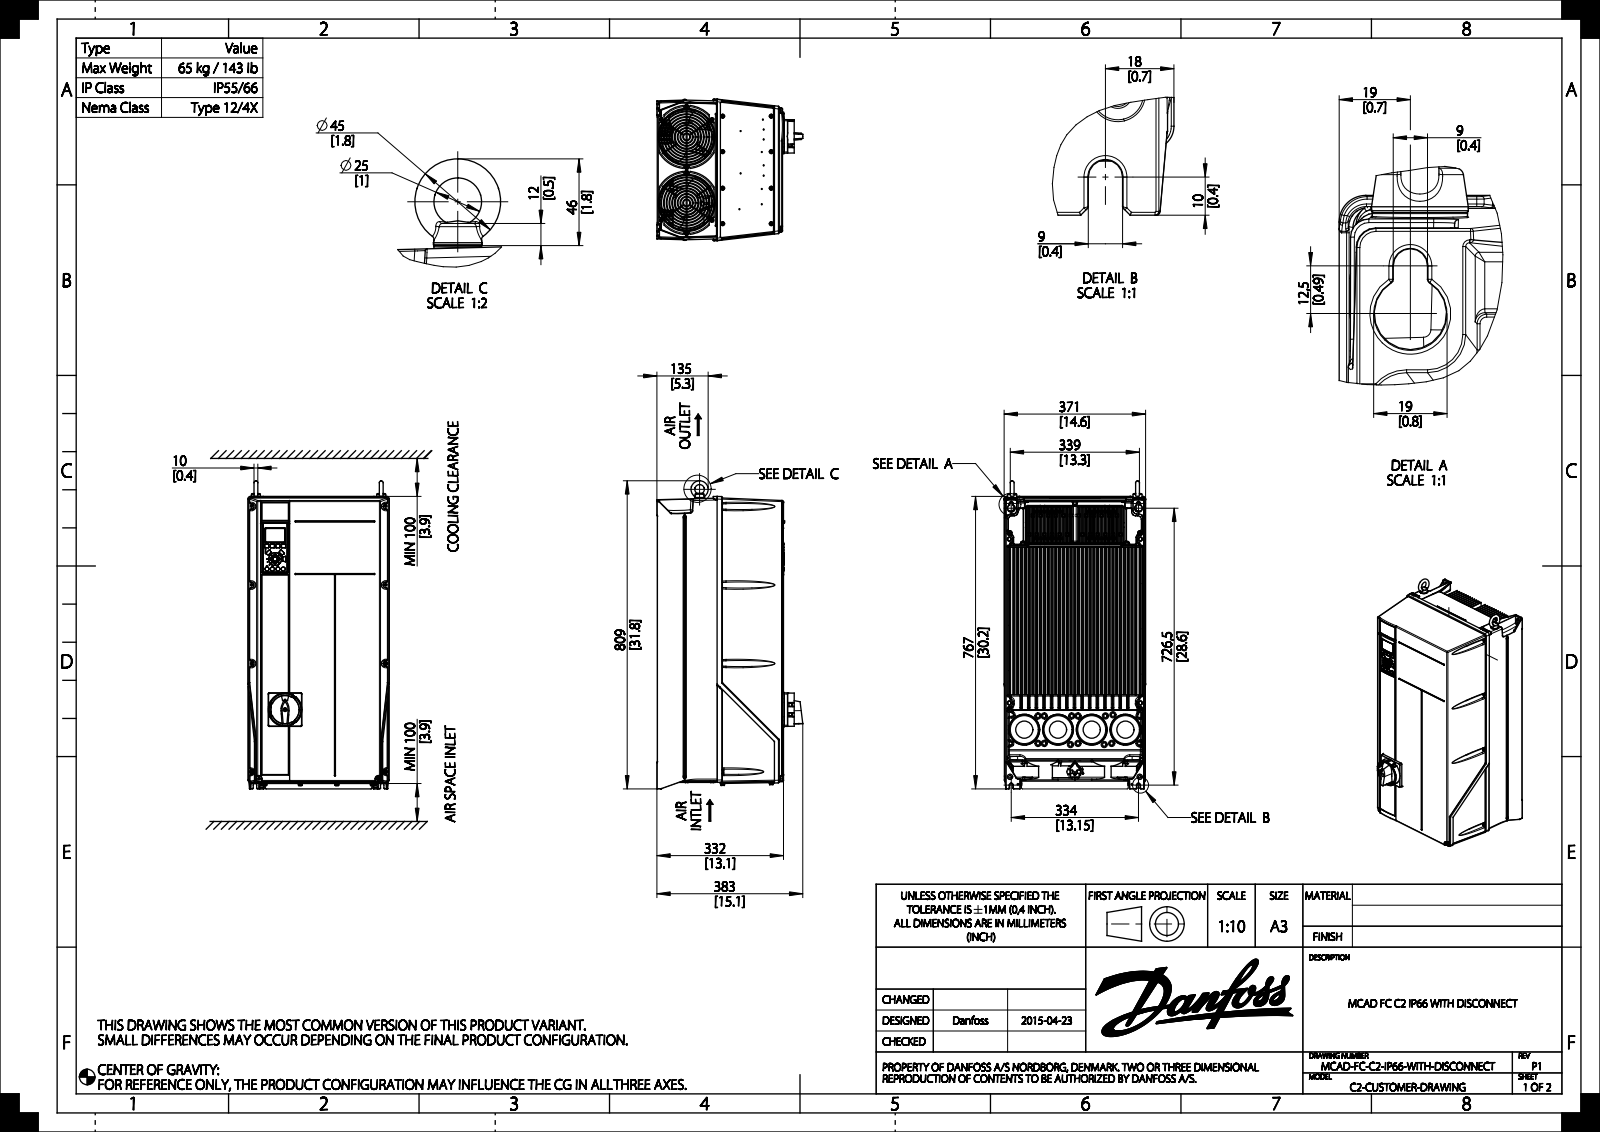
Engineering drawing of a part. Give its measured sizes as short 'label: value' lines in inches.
name: PRT0006
written by: CREO PARAMETRIC BY PTC INC, 2018070 (CONFIG_CONTROL_DESIGN)
unit: in
bodies: 0 solids, 6964 faces (1701 planar, 2613 cylindrical, 2650 other)
size: 30.216 × 15.48 × 14.621
holes: 17× ⌀0.197, 15× ⌀0.165, 12× ⌀0.217, 8× ⌀0.173, 8× ⌀0.179, 3× ⌀0.079, 3× ⌀0.138, 2× ⌀0.181, 2× ⌀0.185, 2× ⌀0.236, 1× ⌀0.472
bosses: 18× ⌀0.394, 18× ⌀0.165, 10× ⌀0.331, 10× ⌀0.197, 9× ⌀0.091, 8× ⌀0.335, 8× ⌀0.315, 8× ⌀0.217
rounds: 258× R0.039, 134× R0.02, 105× R0.098, 89× R0.031, 87× R0.118, 83× R0.028, 81× R0.012, 75× R0.03
face distances: 0.787, 1.575, 2.362, 3.15, 3.937, 4.724, 5.512, 6.299, 7.087, 7.874
hole spacings: 7.441, 3.661, 5.02, 6.213, 8.976, 15.532, 8.091, 8.13
